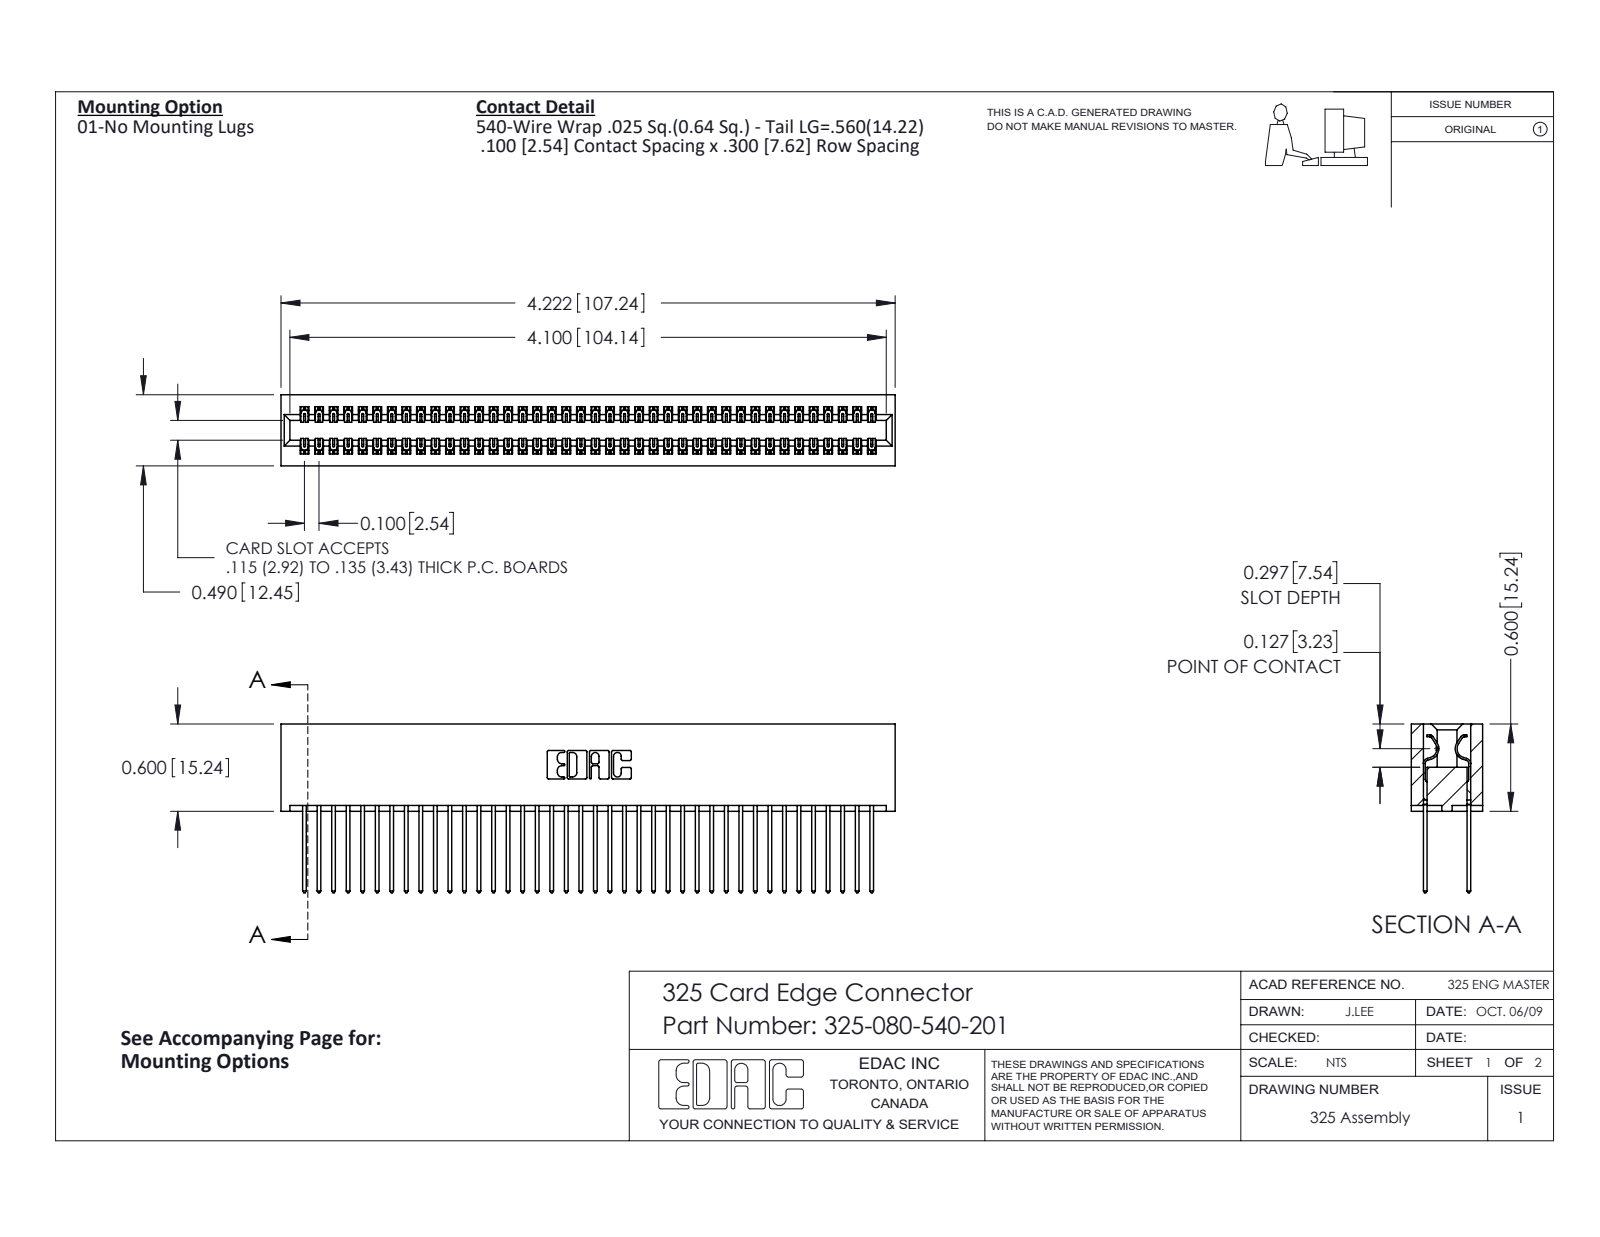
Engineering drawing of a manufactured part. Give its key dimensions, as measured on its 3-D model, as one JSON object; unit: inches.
{"part_name": "325-080-540-201; 325-292-001_325-293-140; 325 Part_Lugless", "step_written_by": "SolidWorks 2016 (CONFIG_CONTROL_DESIGN)", "units": "inches", "bodies": {"solids": 81, "faces": 4266, "planar": 2946, "cylindrical": 1320, "other": 0}, "overall_size": [4.222, 1.16, 0.49], "volume_in3": 0.899, "surface_area_in2": 30.83, "partial_cylinders_radius": [[0.006, 120], [0.01, 80], [0.01, 22], [0.007, 6], [0.031, 6], [0.026, 3], [0.014, 2], [0.022, 2]], "face_to_face_distances": [0.083, 0.407, 0.3, 0.107, 0.383, 0.025, 0.325, 0.49, 0.275, 0.56]}
